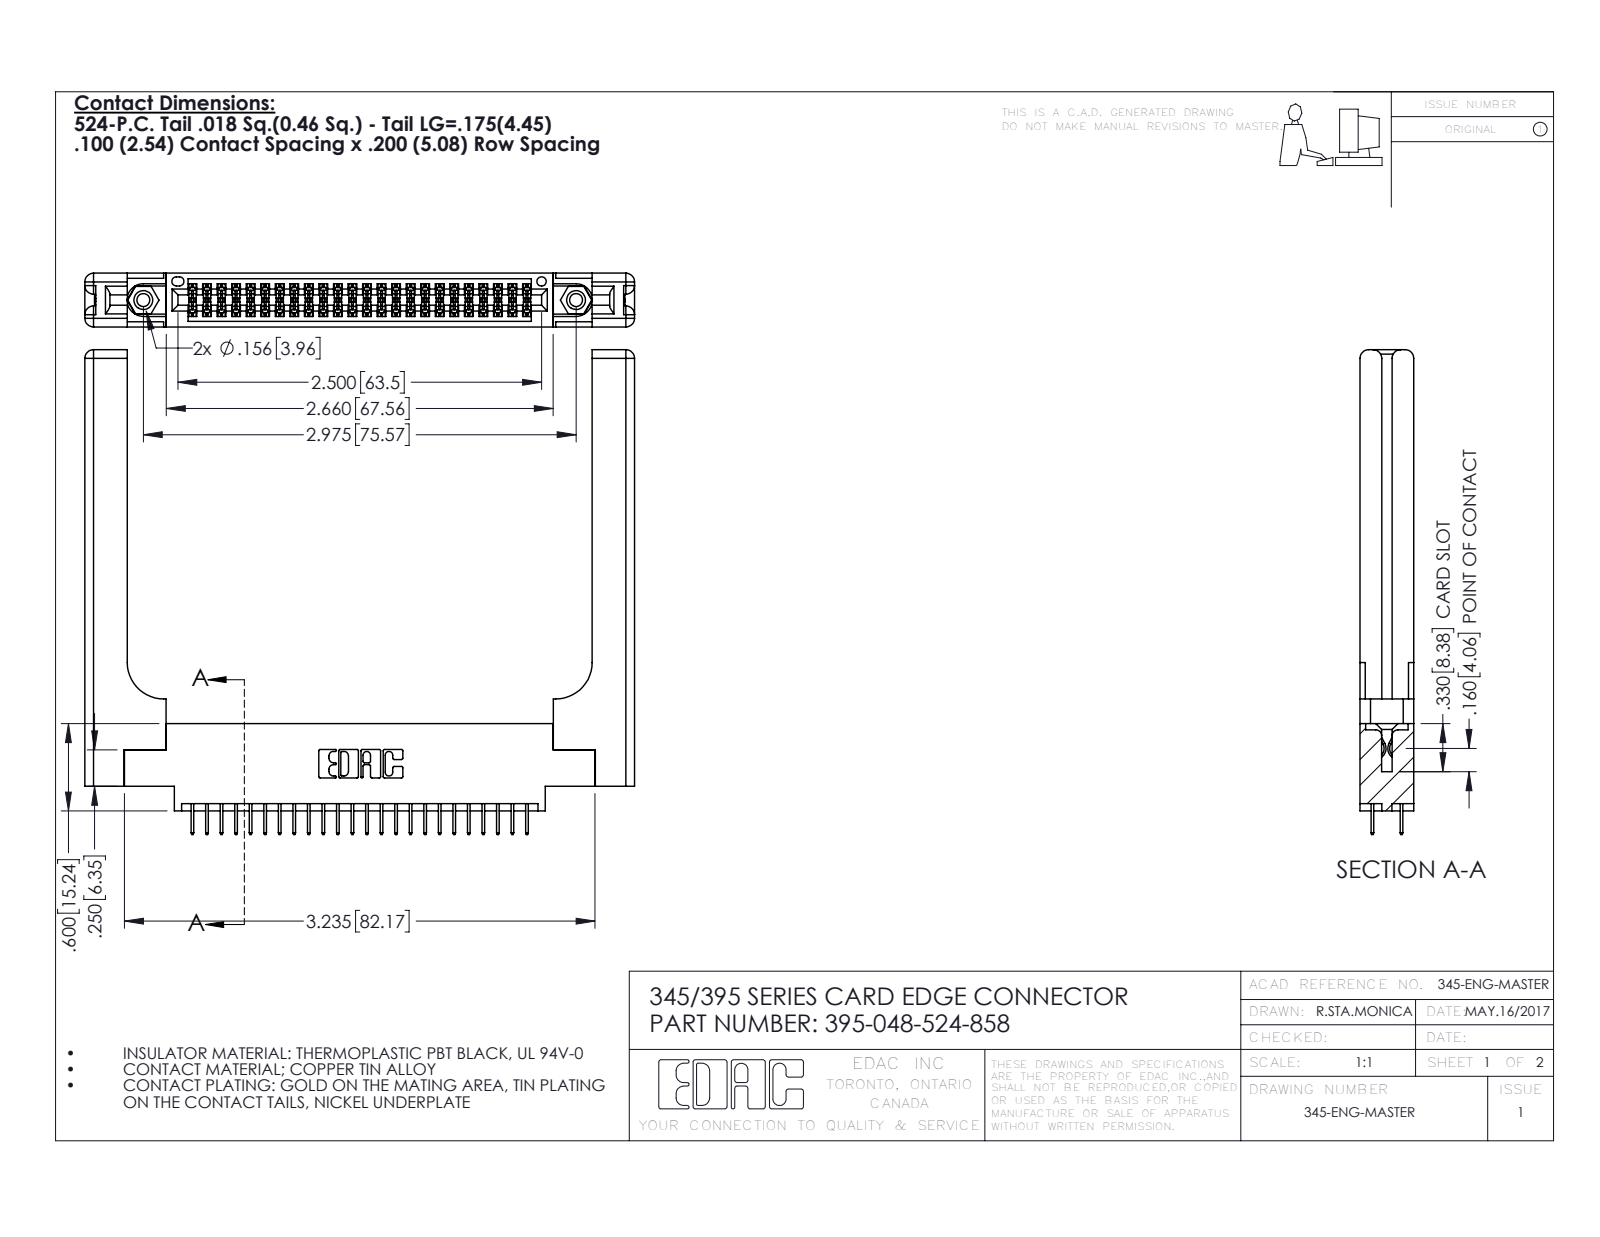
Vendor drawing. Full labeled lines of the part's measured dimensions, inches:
Part name (STEP PRODUCT): 395-048-524-858; 345 Part_0.170 Offset - 0.156 Dia-TH; 345-250-001_345-250-001-102; 345-220-058_345-220-058 (+1 more)
STEP written by: SolidWorks 2016 (CONFIG_CONTROL_DESIGN)
Units: inches
Bodies: 53 solids, 2978 faces (2104 planar, 814 cylindrical, 60 other)
Overall size (bounding box): 3.779 × 3.332 × 0.37
Volume: 1.065 in³ · Surface area: 27.78 in²
Round holes (diameter × count): ⌀0.089 ×2, ⌀0.125 ×2, ⌀0.156 ×2, ⌀0.064 ×1
Round bosses / shafts (diameter × count): ⌀0.155 ×2
Partial cylindrical surfaces — rounded edges, fillets, slot ends (radius × count): R0.006 ×72, R0.01 ×22, R0.06 ×16, R0.007 ×6, R0.031 ×6, R0.026 ×3, R0.014 ×2, R0.019 ×2
Main face-to-face distances: 0.37, 0.072, 0.298, 0.2, 0.148, 0.15, 0.098, 0.272, 0.025, 0.123
Hole centre spacings: 0.27, 2.741, 2.975
